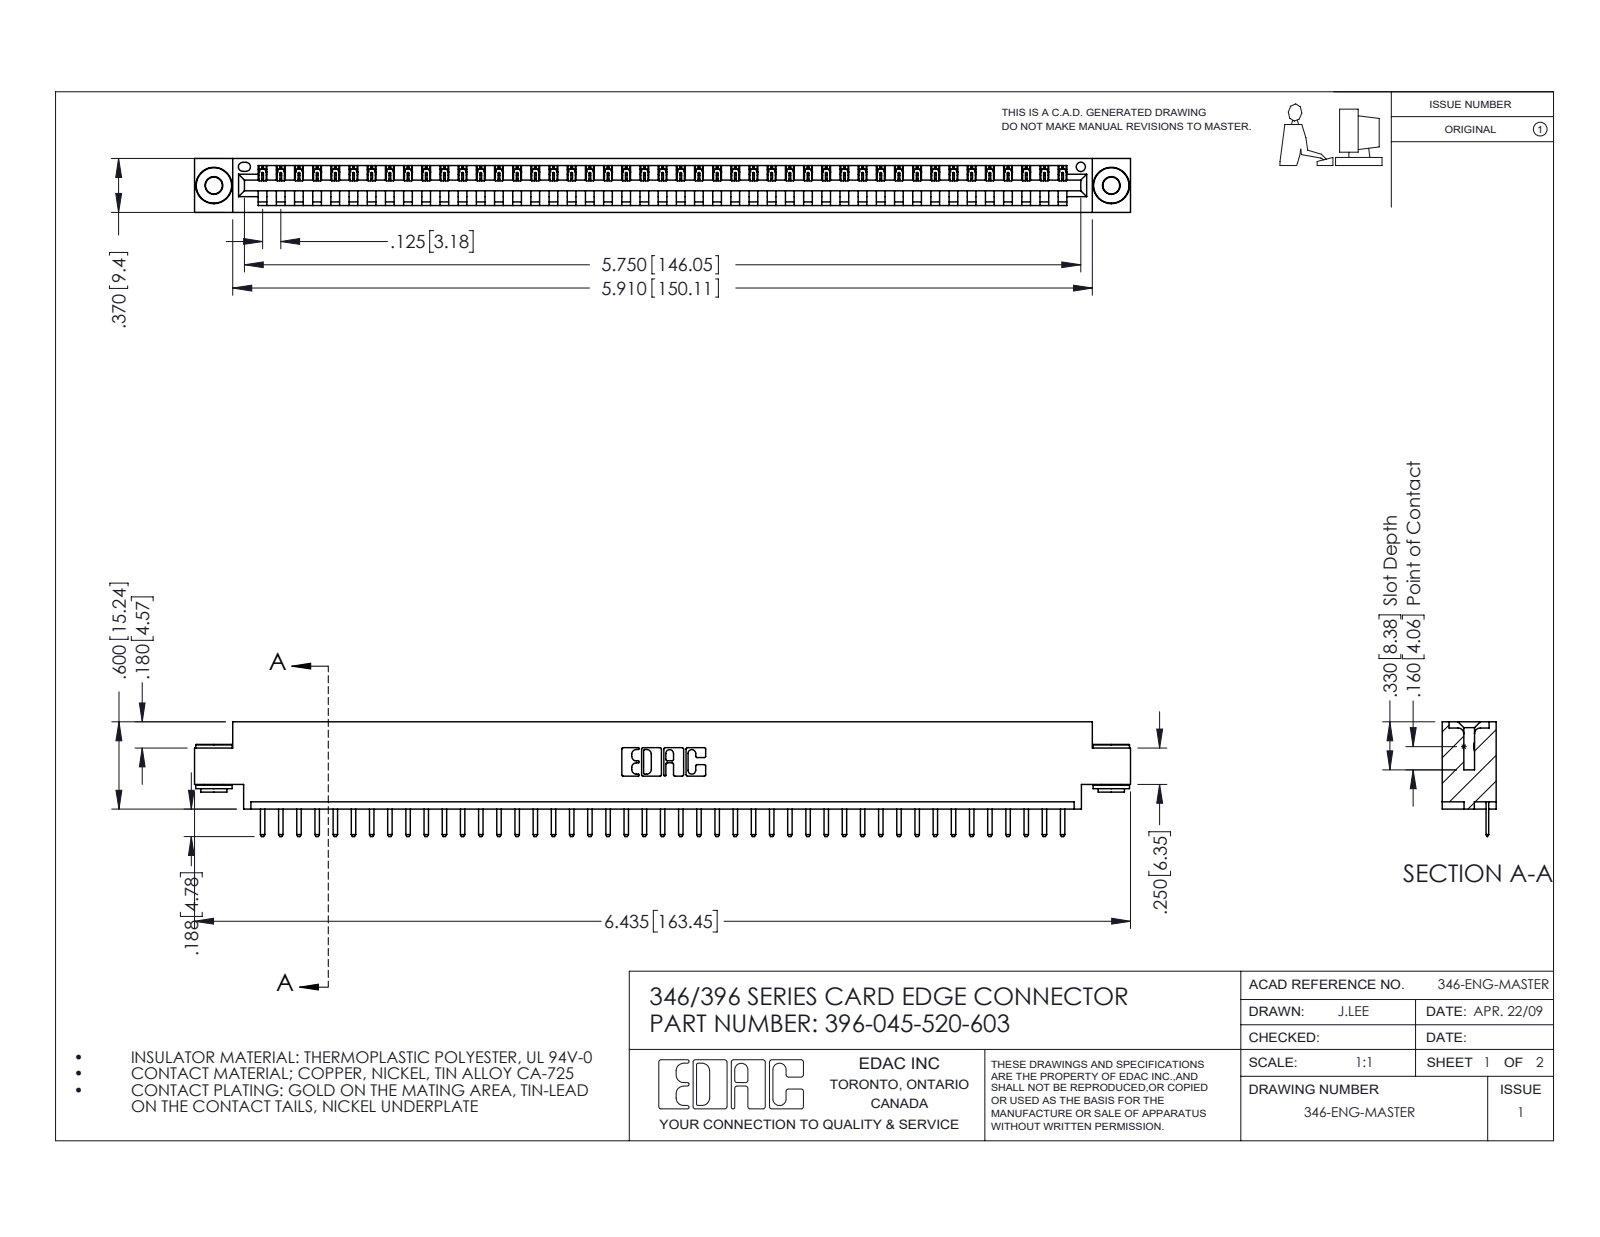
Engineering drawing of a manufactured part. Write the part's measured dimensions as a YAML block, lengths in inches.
part_name: "345-292-001_345-293-120; 346 Part_0.170 Offset - 0.156 Dia-TH; 396-045-520-603; 345-250-002_345-250-002-102"
step_written_by: "SolidWorks 2016 (CONFIG_CONTROL_DESIGN)"
units: inches
bodies: {solids: 48, faces: 2954, planar: 1980, cylindrical: 966, other: 8}
overall_size: [6.435, 0.788, 0.37]
volume: 0.94
surface_area: 29.81
round_holes:
  - {diameter: 0.116, count: 2}
  - {diameter: 0.156, count: 2}
  - {diameter: 0.064, count: 1}
round_bosses_or_shafts:
  - {diameter: 0.25, count: 2}
  - {diameter: 0.18, count: 2}
  - {diameter: 0.136, count: 2}
partial_cylinders:
  - {radius: 0.01, count: 92}
  - {radius: 0.006, count: 90}
  - {radius: 0.01, count: 22}
  - {radius: 0.007, count: 6}
  - {radius: 0.031, count: 6}
  - {radius: 0.026, count: 3}
  - {radius: 0.031, count: 2}
  - {radius: 0.04, count: 2}
face_to_face_distances: [0.048, 0.322, 0.37, 0.25, 0.025, 0.148, 0.222, 0.1, 0.174, 0.072]
hole_center_spacings: [0.246, 5.961, 6.17]
